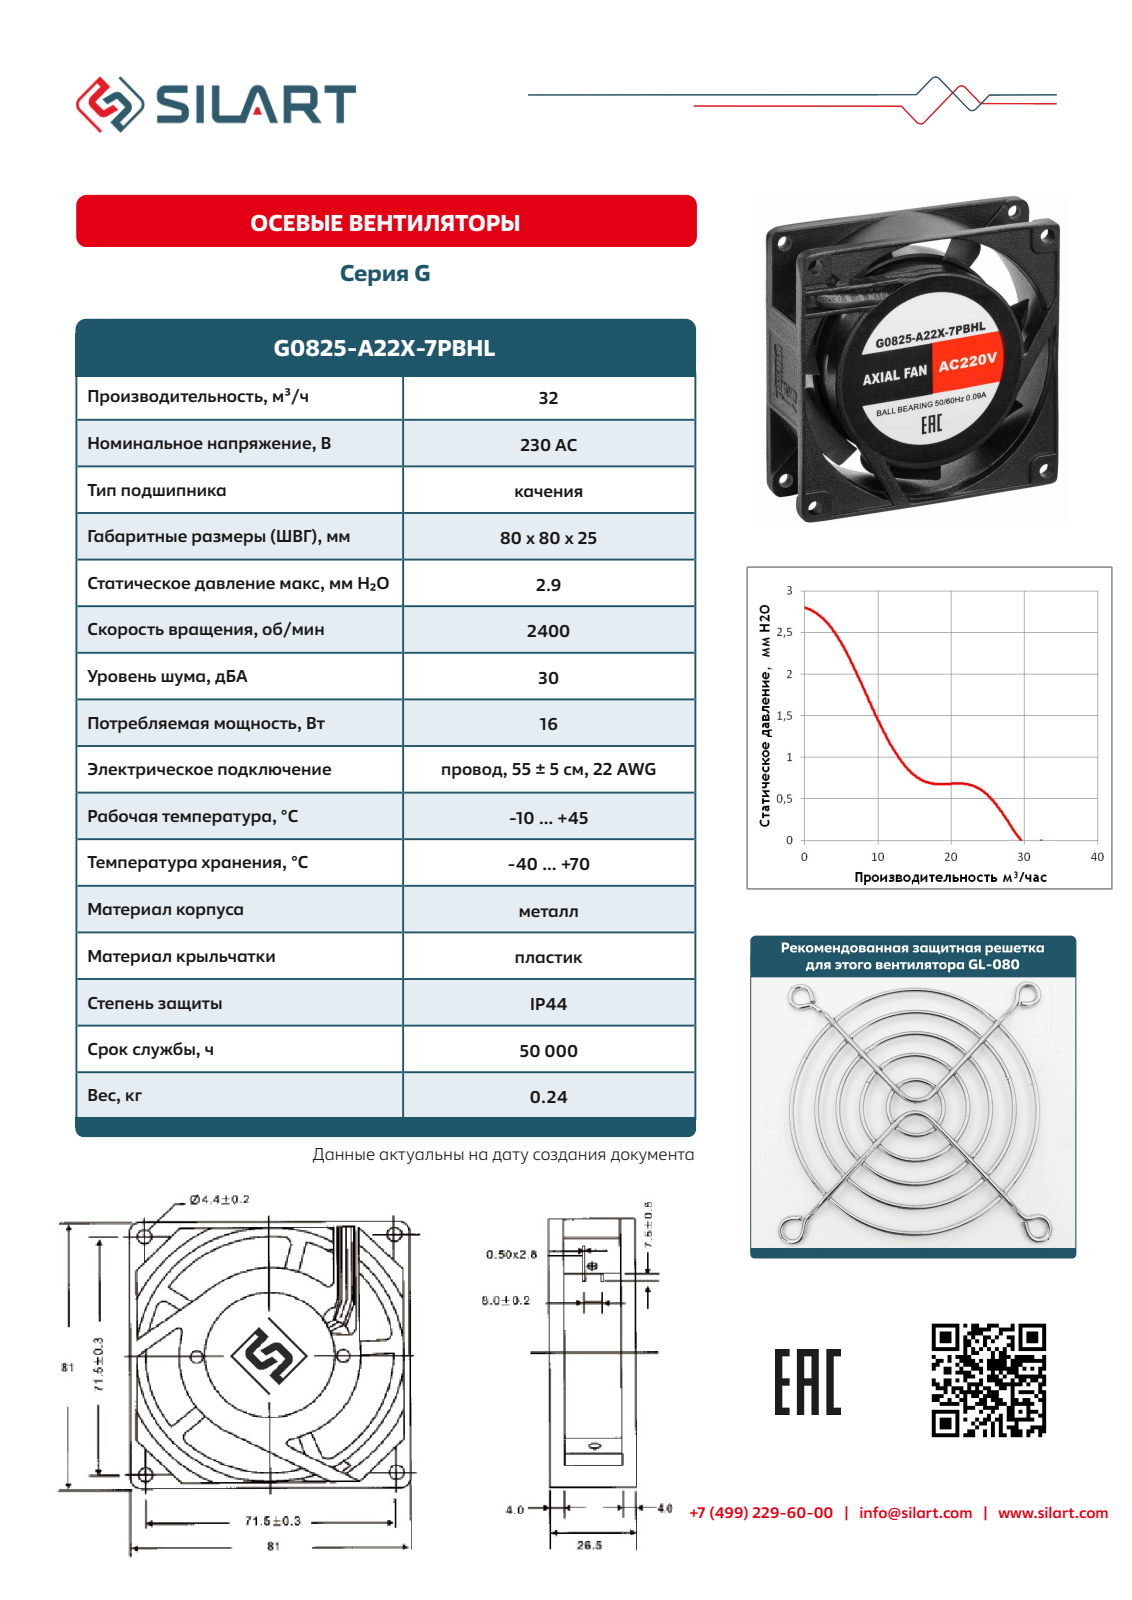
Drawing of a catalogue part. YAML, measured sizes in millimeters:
part_name: "G0825-A22X-7PBHL v16"
step_written_by: "Autodesk Translation Framework v11.17.0.187 (AUTOMOTIVE_DESIGN)"
units: millimeters
bodies: {solids: 2, faces: 1112, planar: 410, cylindrical: 247, other: 455}
overall_size: [81, 81, 26.1]
volume: 75696
surface_area: 51856
round_holes:
  - {diameter: 4.4, count: 4}
  - {diameter: 3.17, count: 2}
  - {diameter: 3.5, count: 2}
  - {diameter: 3.57, count: 2}
  - {diameter: 58, count: 1}
  - {diameter: 60, count: 1}
  - {diameter: 77.5, count: 1}
round_bosses_or_shafts:
  - {diameter: 3.9, count: 2}
  - {diameter: 55, count: 1}
  - {diameter: 53.87, count: 1}
  - {diameter: 52.46, count: 1}
  - {diameter: 2, count: 1}
partial_cylinders:
  - {radius: 3, count: 37}
  - {radius: 0.6, count: 29}
  - {radius: 0.5, count: 18}
  - {radius: 0.1, count: 14}
  - {radius: 0.4, count: 11}
  - {radius: 2, count: 8}
  - {radius: 1, count: 2}
  - {radius: 4.63, count: 1}
face_to_face_distances: [1, 0.5, 1.5, 2, 21.5, 20, 22, 21, 23, 19.5]
hole_center_spacings: [50.56, 71.5, 4.5, 85.5, 85.62, 101.12]
